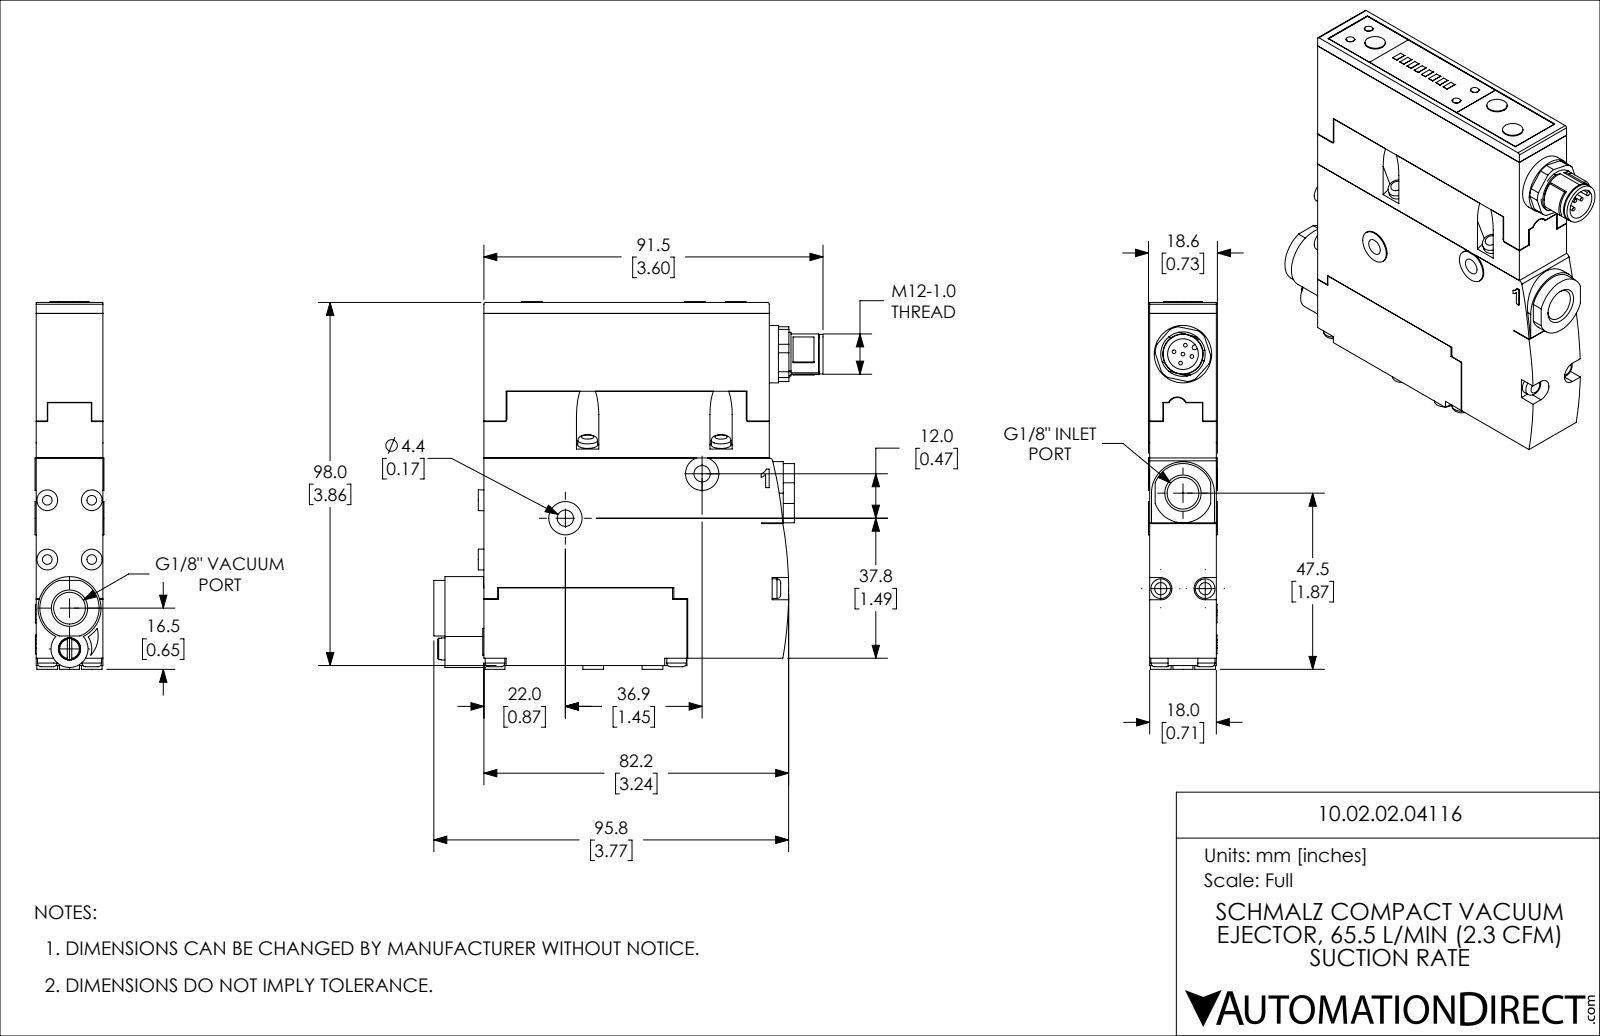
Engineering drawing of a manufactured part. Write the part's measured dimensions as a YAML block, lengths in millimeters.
part_name: "10.02.02.04116"
step_written_by: "SolidWorks 2021 (CONFIG_CONTROL_DESIGN)"
units: millimeters
bodies: {solids: 11, faces: 614, planar: 345, cylindrical: 213, other: 56}
overall_size: [105, 99.15, 18.6]
volume: 143599
surface_area: 45857
round_holes:
  - {diameter: 2.6, count: 8}
  - {diameter: 3.4, count: 8}
  - {diameter: 4.4, count: 2}
  - {diameter: 8.57, count: 2}
  - {diameter: 12, count: 2}
  - {diameter: 6, count: 1}
  - {diameter: 8.3, count: 1}
  - {diameter: 12.1, count: 1}
round_bosses_or_shafts:
  - {diameter: 2.2, count: 10}
  - {diameter: 5.6, count: 8}
  - {diameter: 5.3, count: 8}
  - {diameter: 1, count: 5}
  - {diameter: 2.3, count: 4}
  - {diameter: 5.5, count: 3}
  - {diameter: 11.9, count: 2}
  - {diameter: 9, count: 2}
partial_cylinders:
  - {radius: 3, count: 6}
  - {radius: 0.2, count: 4}
  - {radius: 2.65, count: 3}
  - {radius: 0.5, count: 2}
  - {radius: 0.75, count: 2}
  - {radius: 8, count: 2}
  - {radius: 105, count: 2}
  - {radius: 0.6, count: 1}
face_to_face_distances: [18, 21, 39, 74, 35, 53, 76.85, 41.85, 23.85, 2.85]
hole_center_spacings: [12, 16, 20, 6.29, 6.5, 7.85, 7.97, 13.65]
